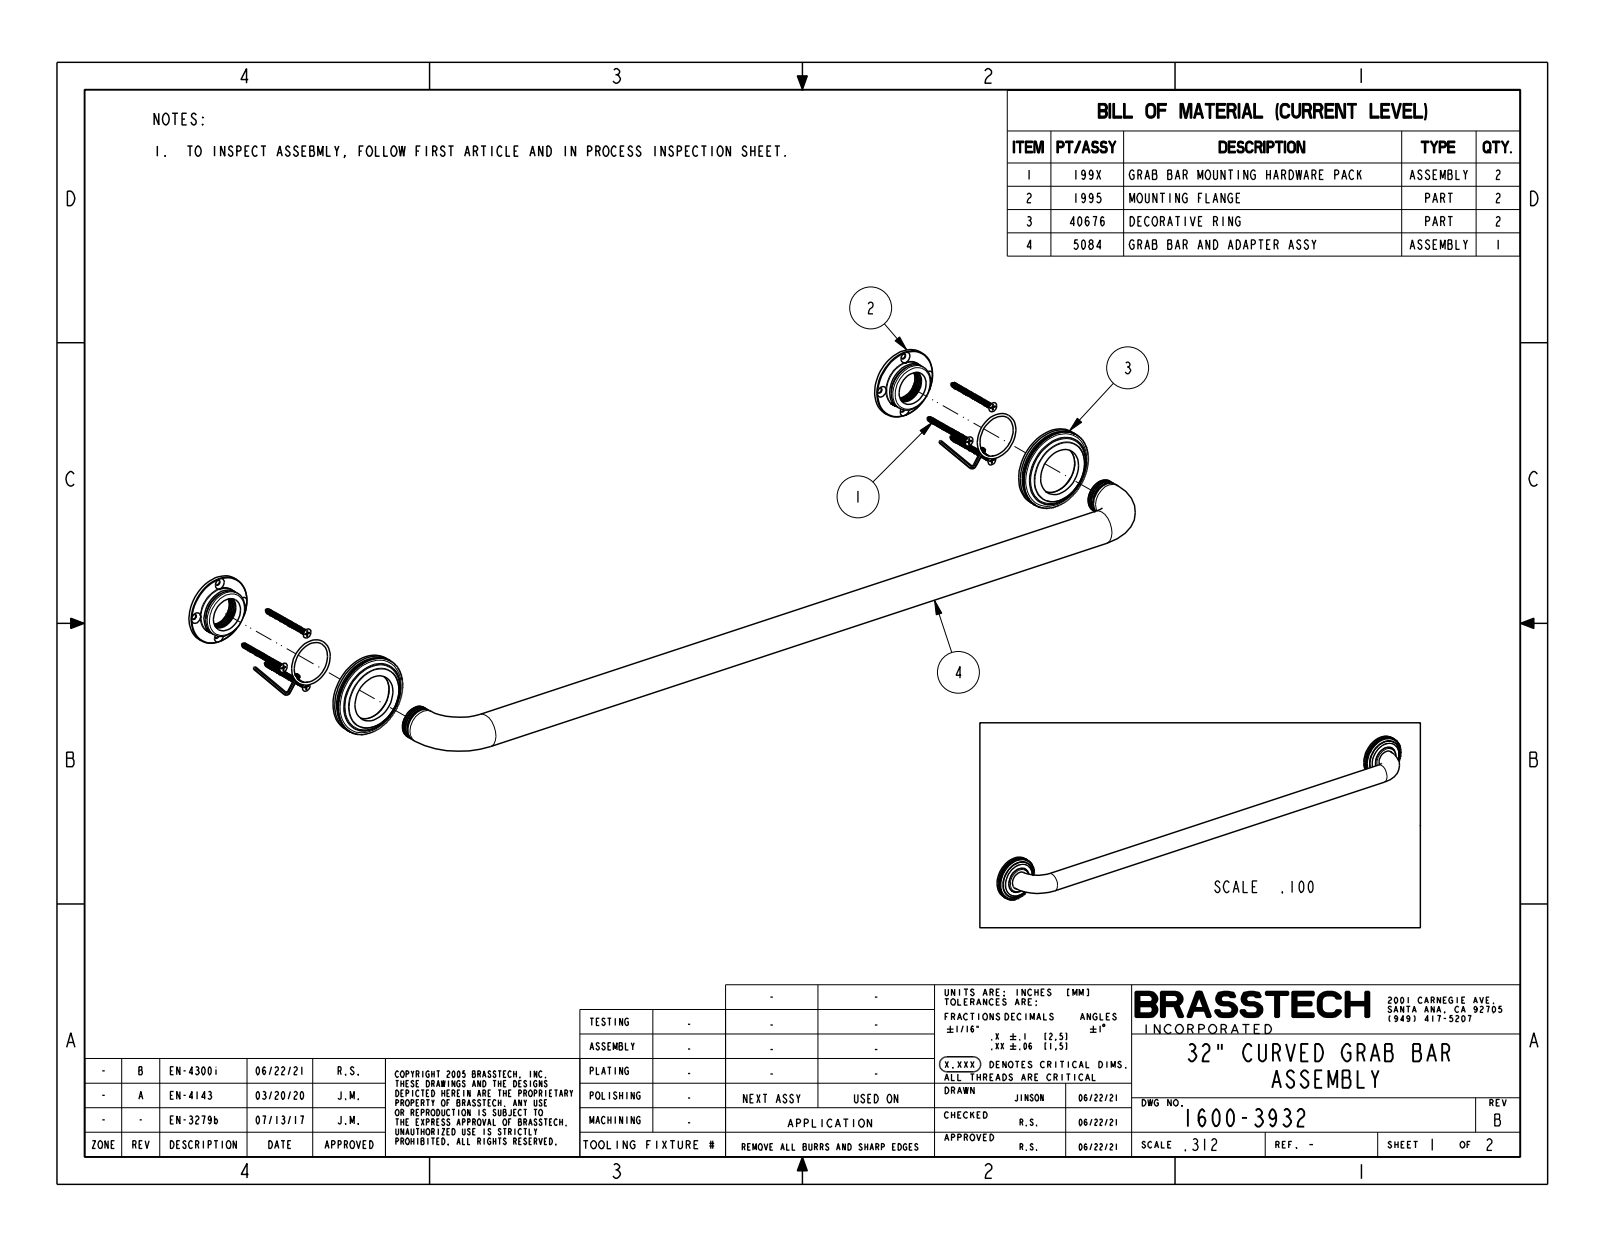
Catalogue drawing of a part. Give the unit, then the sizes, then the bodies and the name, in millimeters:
Units: millimetres
Overall size (bounding box): 889 × 76.2 × 69.9
Round bosses / shafts (diameter × count): ⌀76.2 ×2, ⌀73.7 ×2, ⌀44.5 ×2, ⌀31.8 ×1
Main face-to-face distances: 13.3, 15.2, 1.9, 8.3, 5.1, 7, 2.5, 6.4, 1.9, 7
Volume: 789 200 mm³ · Surface area: 108 100 mm²
Bodies: 1 solid, 1134 faces (732 planar, 374 cylindrical, 28 other)
Part name (STEP PRODUCT): 1600-3932
STEP written by: CREO PARAMETRIC BY PTC INC, 2018400 (CONFIG_CONTROL_DESIGN)
